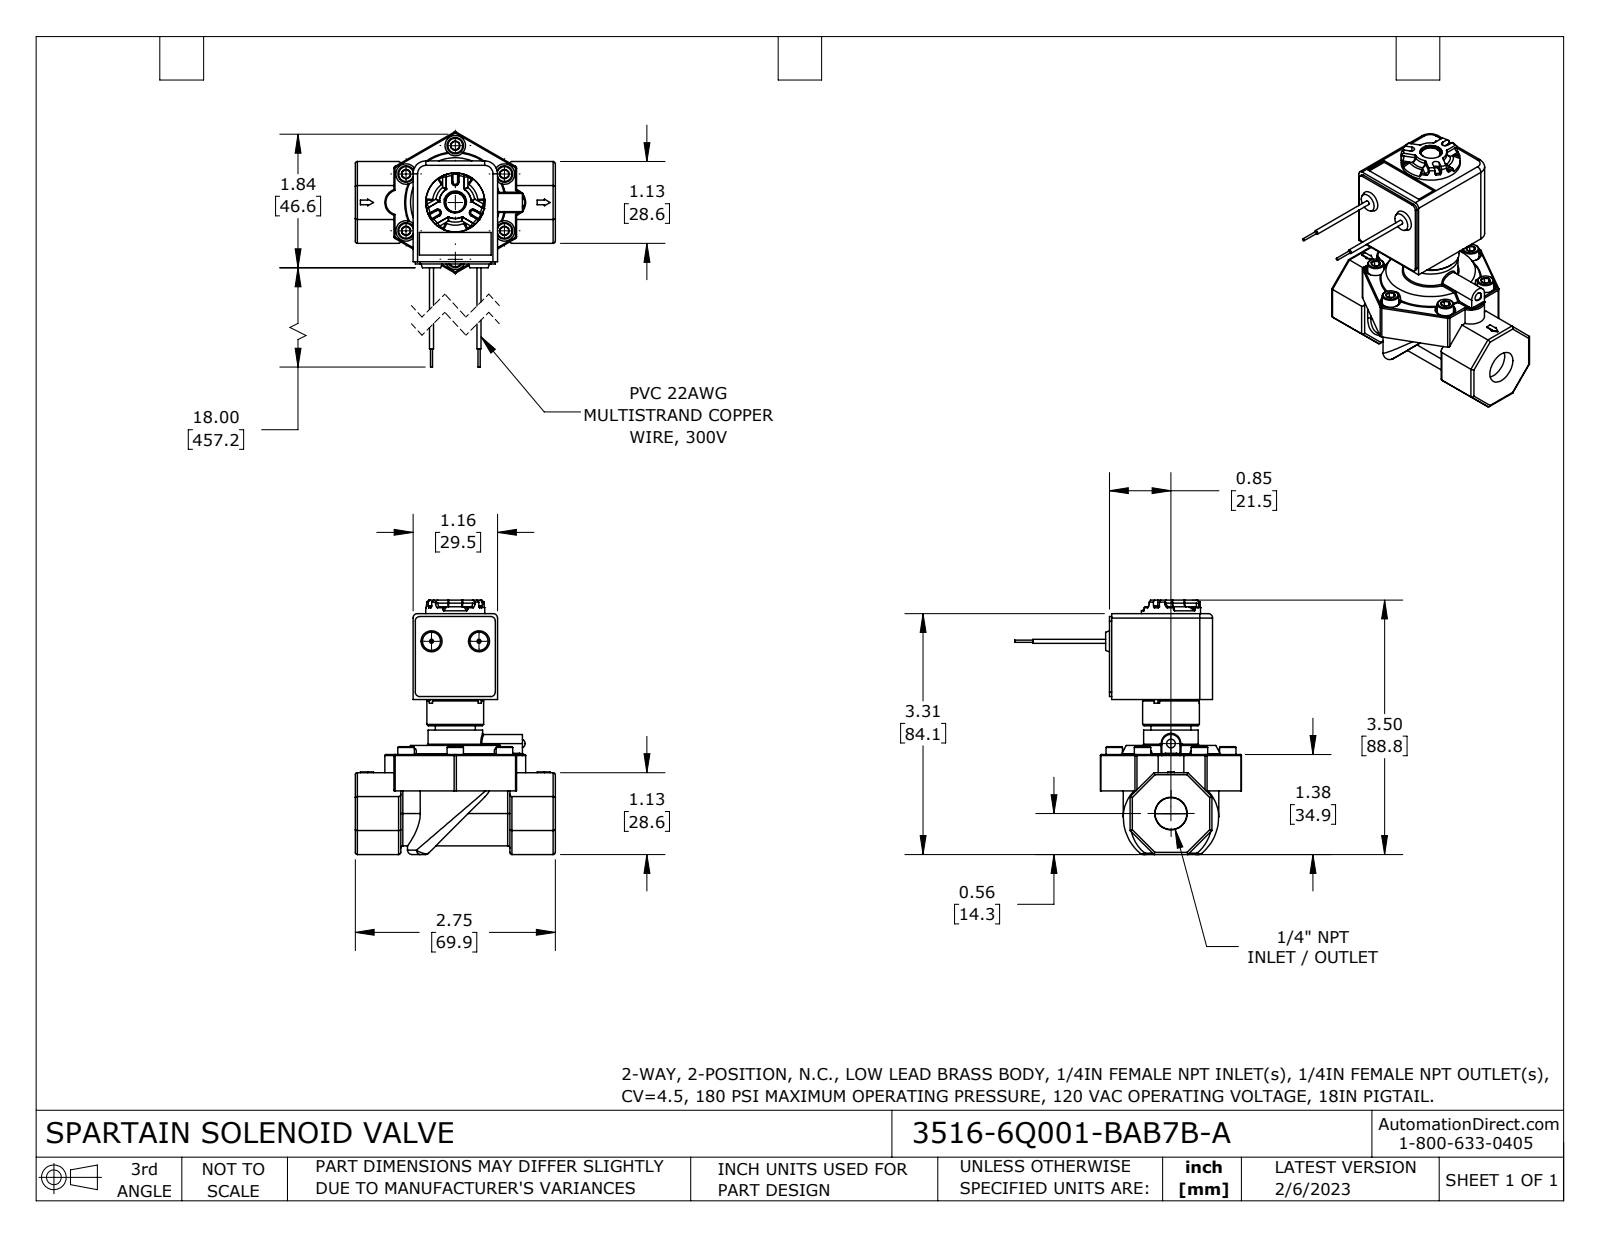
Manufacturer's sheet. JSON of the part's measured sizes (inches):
{"part_name": "3516-6Q001-BAB7B-A", "step_written_by": "SolidWorks 2021 (CONFIG_CONTROL_DESIGN)", "units": "inches", "bodies": {"solids": 2, "faces": 1187, "planar": 236, "cylindrical": 648, "other": 303}, "overall_size": [3.497, 3.117, 2.75], "volume_in3": 4.816, "surface_area_in2": 49.34, "round_holes": [[0.104, 6], [0.156, 6], [0.218, 6], [0.281, 6], [0.093, 2], [0.136, 2], [0.047, 1], [0.062, 1], [0.065, 1], [0.09, 1], [0.092, 1], [0.119, 1]], "round_bosses_or_shafts": [[0.212, 7], [0.226, 6], [0.138, 6], [0.097, 6], [0.156, 2], [0.03, 2], [1.29, 1], [0.812, 1]], "partial_cylinders_radius": [[0.03, 30], [0.015, 19], [0.062, 15], [0.125, 9], [0.156, 8], [0.031, 6], [0.05, 6], [0.044, 3]], "face_to_face_distances": [1.125, 0.794, 1.955, 1.161, 0.25, 1.005, 1.687, 0.625, 0.016, 1.021], "hole_center_spacings": [0.781, 1.353, 0.404, 1.105, 1.509, 1.562, 0.71, 0.8]}
